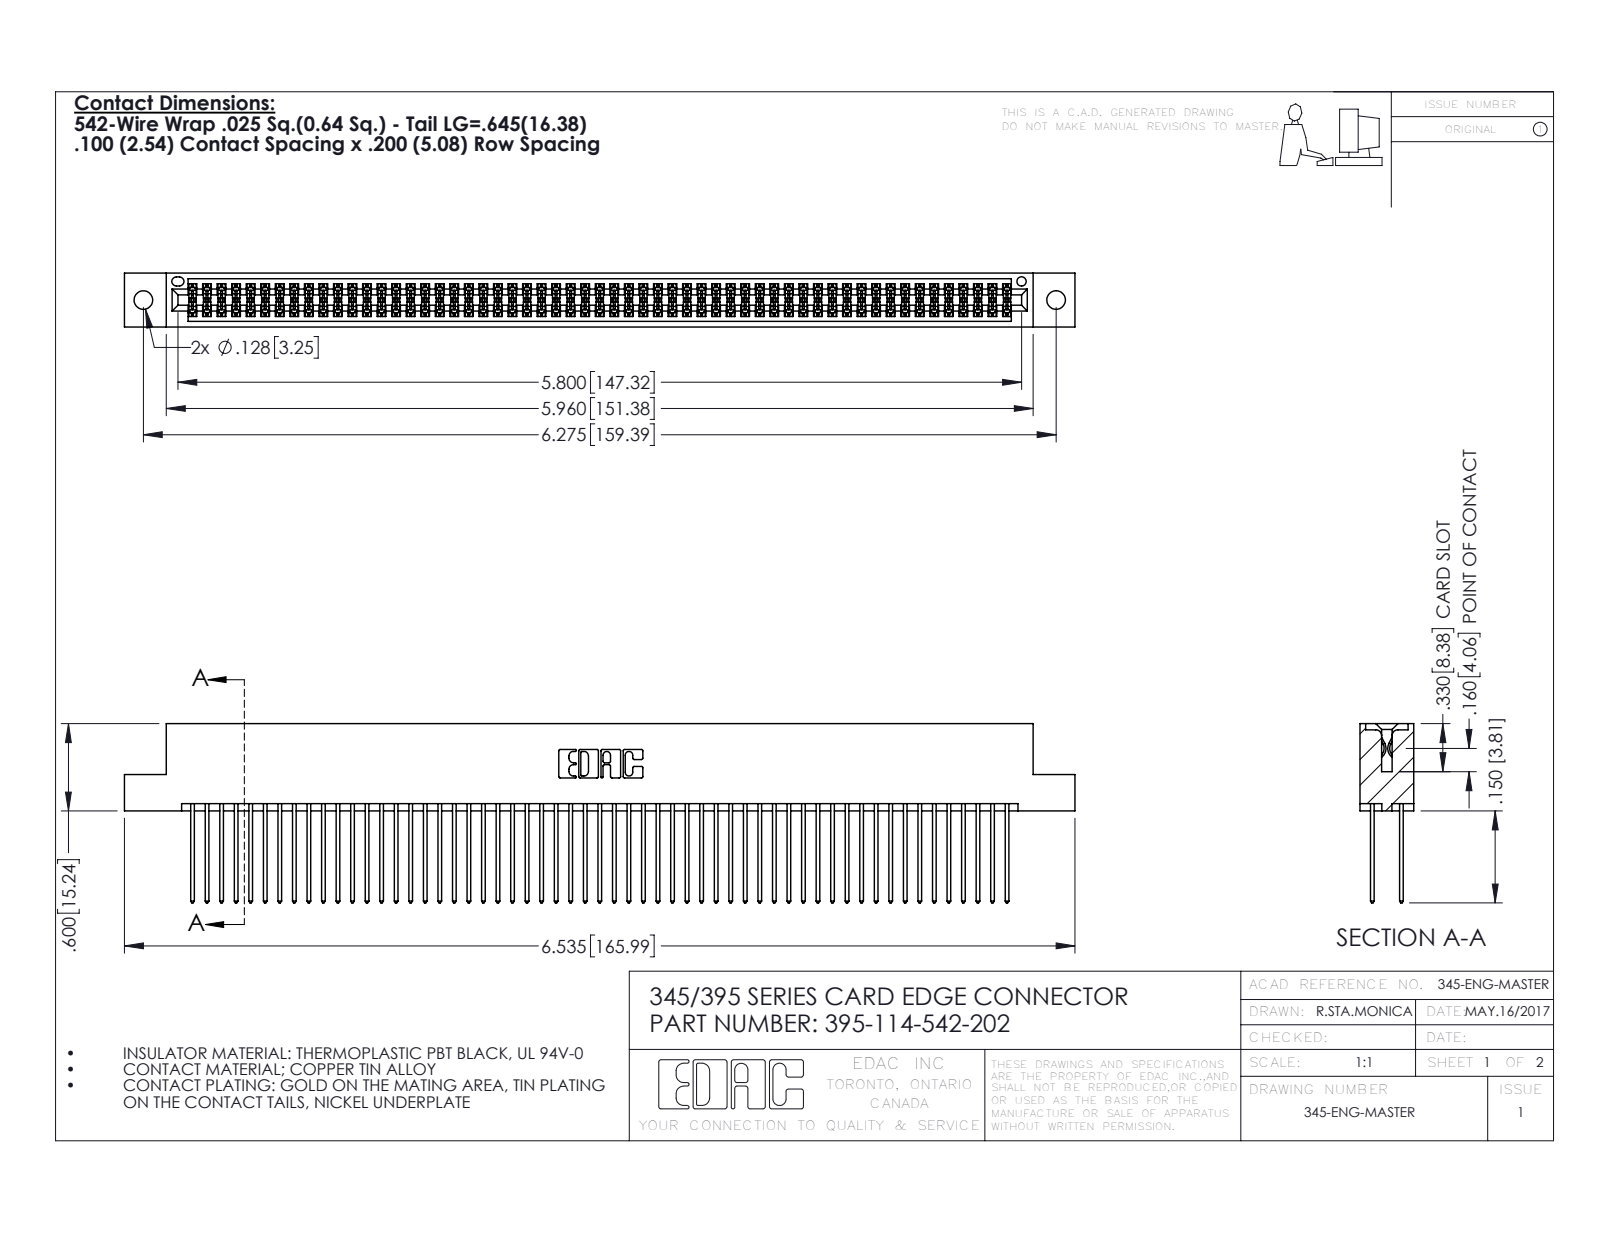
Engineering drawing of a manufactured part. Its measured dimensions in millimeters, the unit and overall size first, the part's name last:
Units: millimetres
Overall size (bounding box): 166 × 31.3 × 9.4
Round holes (diameter × count): ⌀3.3 ×2, ⌀1.6 ×1
Partial cylindrical surfaces — rounded edges, fillets, slot ends (radius × count): R0.2 ×171, R0.3 ×114, R0.3 ×22, R0.2 ×6, R0.8 ×6, R0.7 ×3, R0.4 ×2, R0.5 ×2
Main face-to-face distances: 7.6, 1.8, 5.1, 2.5, 6.9, 0.6, 5.7, 9.4, 4.4, 3.8
Hole centre spacings: 6.9, 153.4, 159.4
Volume: 16 760 mm³ · Surface area: 27 270 mm²
Bodies: 115 solids, 5826 faces (3842 planar, 1984 cylindrical, 0 other)
Part name (STEP PRODUCT): 345 Part_Flush Mounting Lugs - 0.128 Dia; 395-114-542-202; 345-292-001_345-293-142
STEP written by: SolidWorks 2016 (CONFIG_CONTROL_DESIGN)
